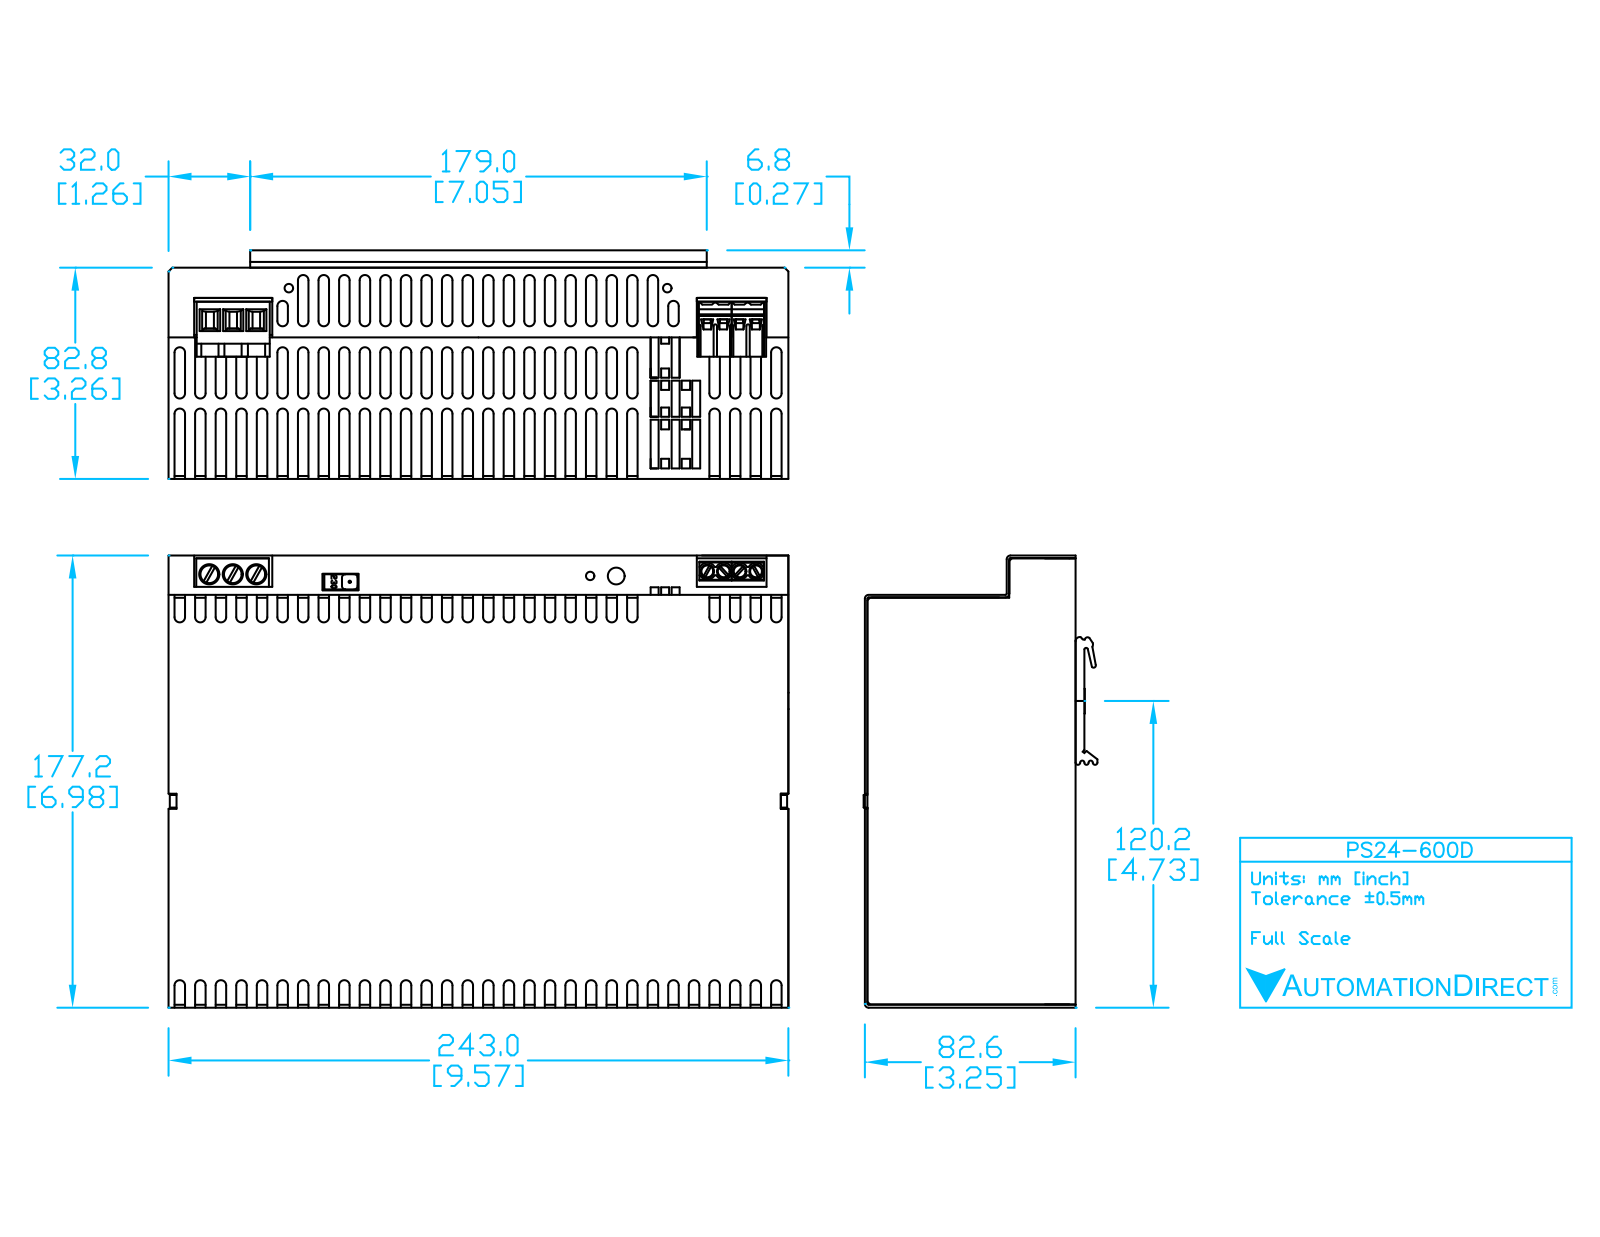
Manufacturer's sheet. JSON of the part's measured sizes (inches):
{"part_name": "PS24-600D", "step_written_by": "SolidWorks 2011 (CONFIG_CONTROL_DESIGN)", "units": "inches", "bodies": {"solids": 1, "faces": 1338, "planar": 661, "cylindrical": 656, "other": 21}, "overall_size": [9.57, 6.98, 3.592], "volume_in3": 88.16, "surface_area_in2": 444.7, "round_holes": [[0.15, 4], [0.25, 3], [0.125, 1]], "round_bosses_or_shafts": [[0.216, 3], [0.3, 1]], "partial_cylinders_radius": [[0.081, 207], [0.03, 14], [0.015, 7], [0.06, 5], [0.02, 3], [0.05, 2], [0.035, 1], [0.04, 1]], "face_to_face_distances": [0.04, 0.08, 3.249, 3.169, 3.209, 3.129, 0.041, 2.495, 0.044, 9.524], "hole_center_spacings": [0.3, 0.4, 0.6, 0.8, 0.9, 1.702, 2.002, 2.302]}
